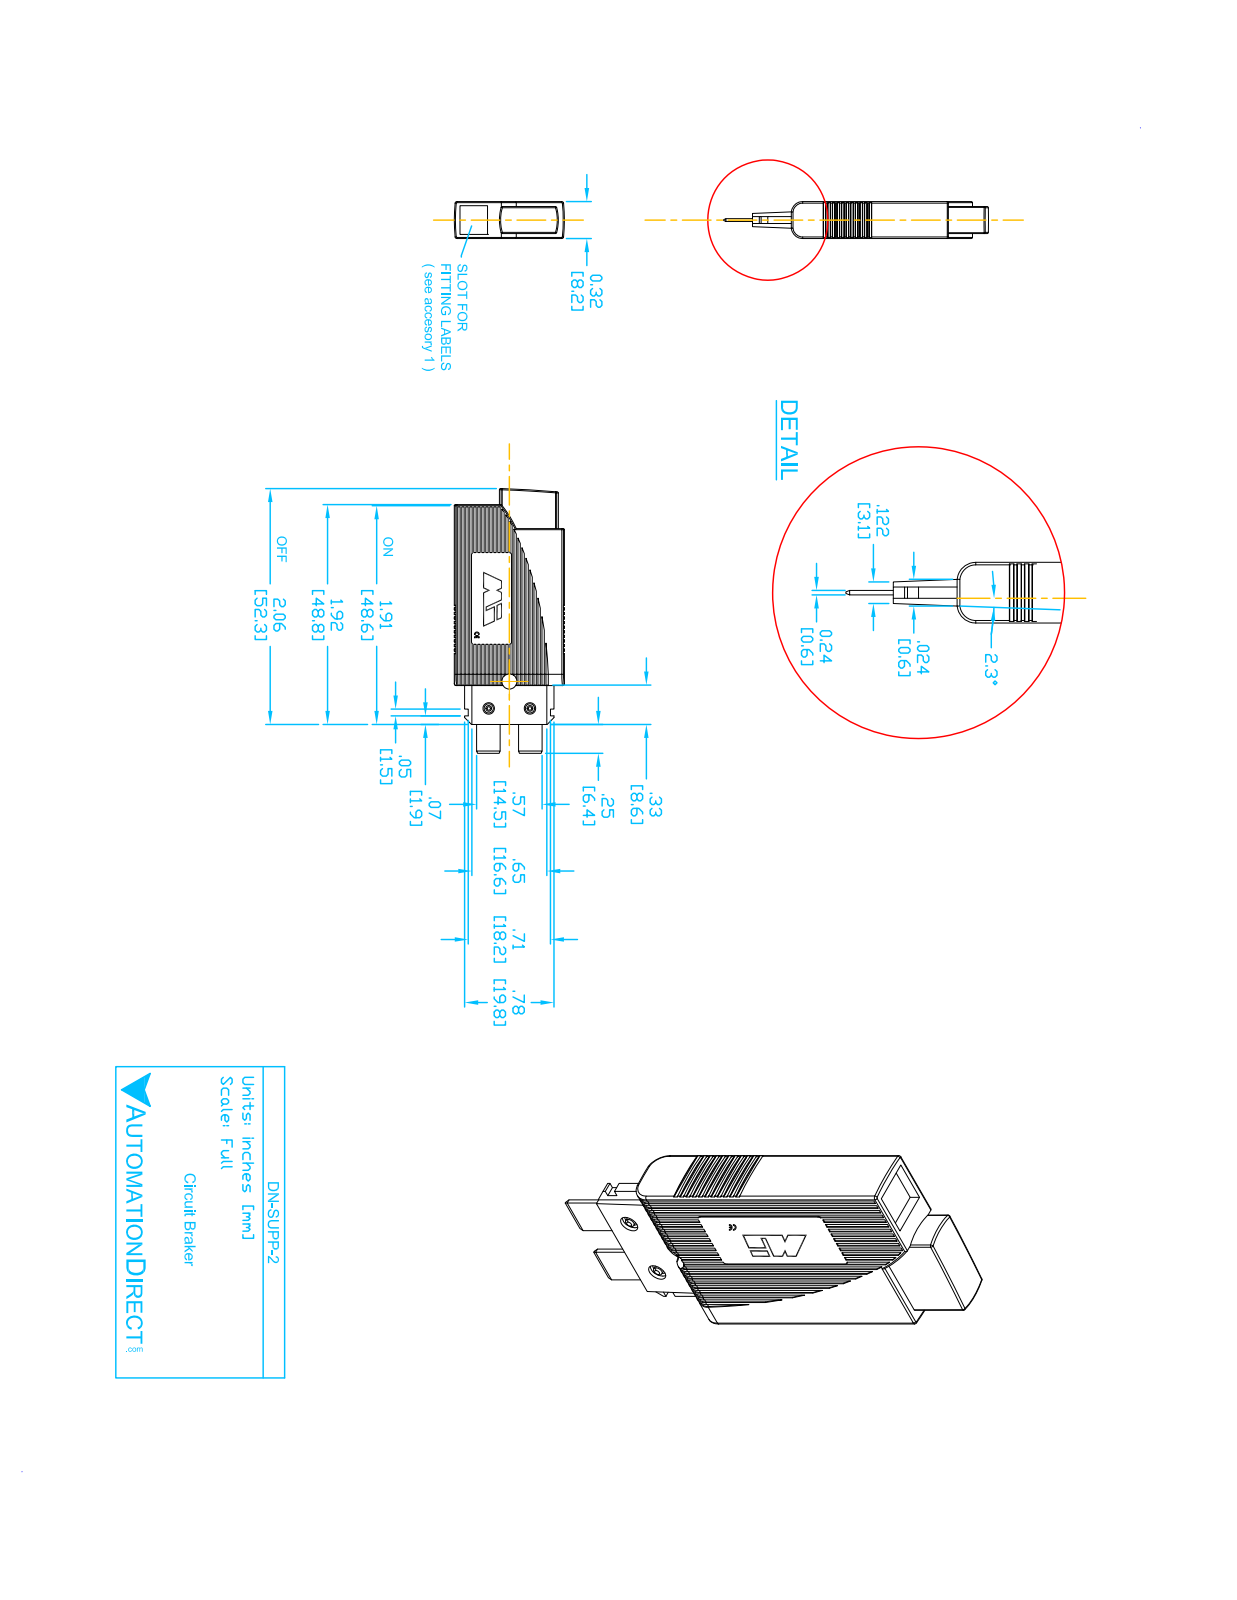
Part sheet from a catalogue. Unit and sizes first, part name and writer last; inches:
Units: inches
Overall size (bounding box): 2.18 × 0.961 × 0.323
Partial cylindrical surfaces — rounded edges, fillets, slot ends (radius × count): R0.012 ×21, R0.157 ×2, R2.165 ×1, R2.331 ×1, R2.362 ×1
Main face-to-face distances: 0.323, 0.961, 0.15, 0.173, 0.031, 0.291, 0.118, 0.142, 0.024, 0.14
Volume: 0.505 in³ · Surface area: 5.231 in²
Bodies: 1 solid, 95 faces (47 planar, 28 cylindrical, 20 other)
Part name (STEP PRODUCT): DN-SUPP-2
STEP written by: SolidWorks 2017 (AUTOMOTIVE_DESIGN)
